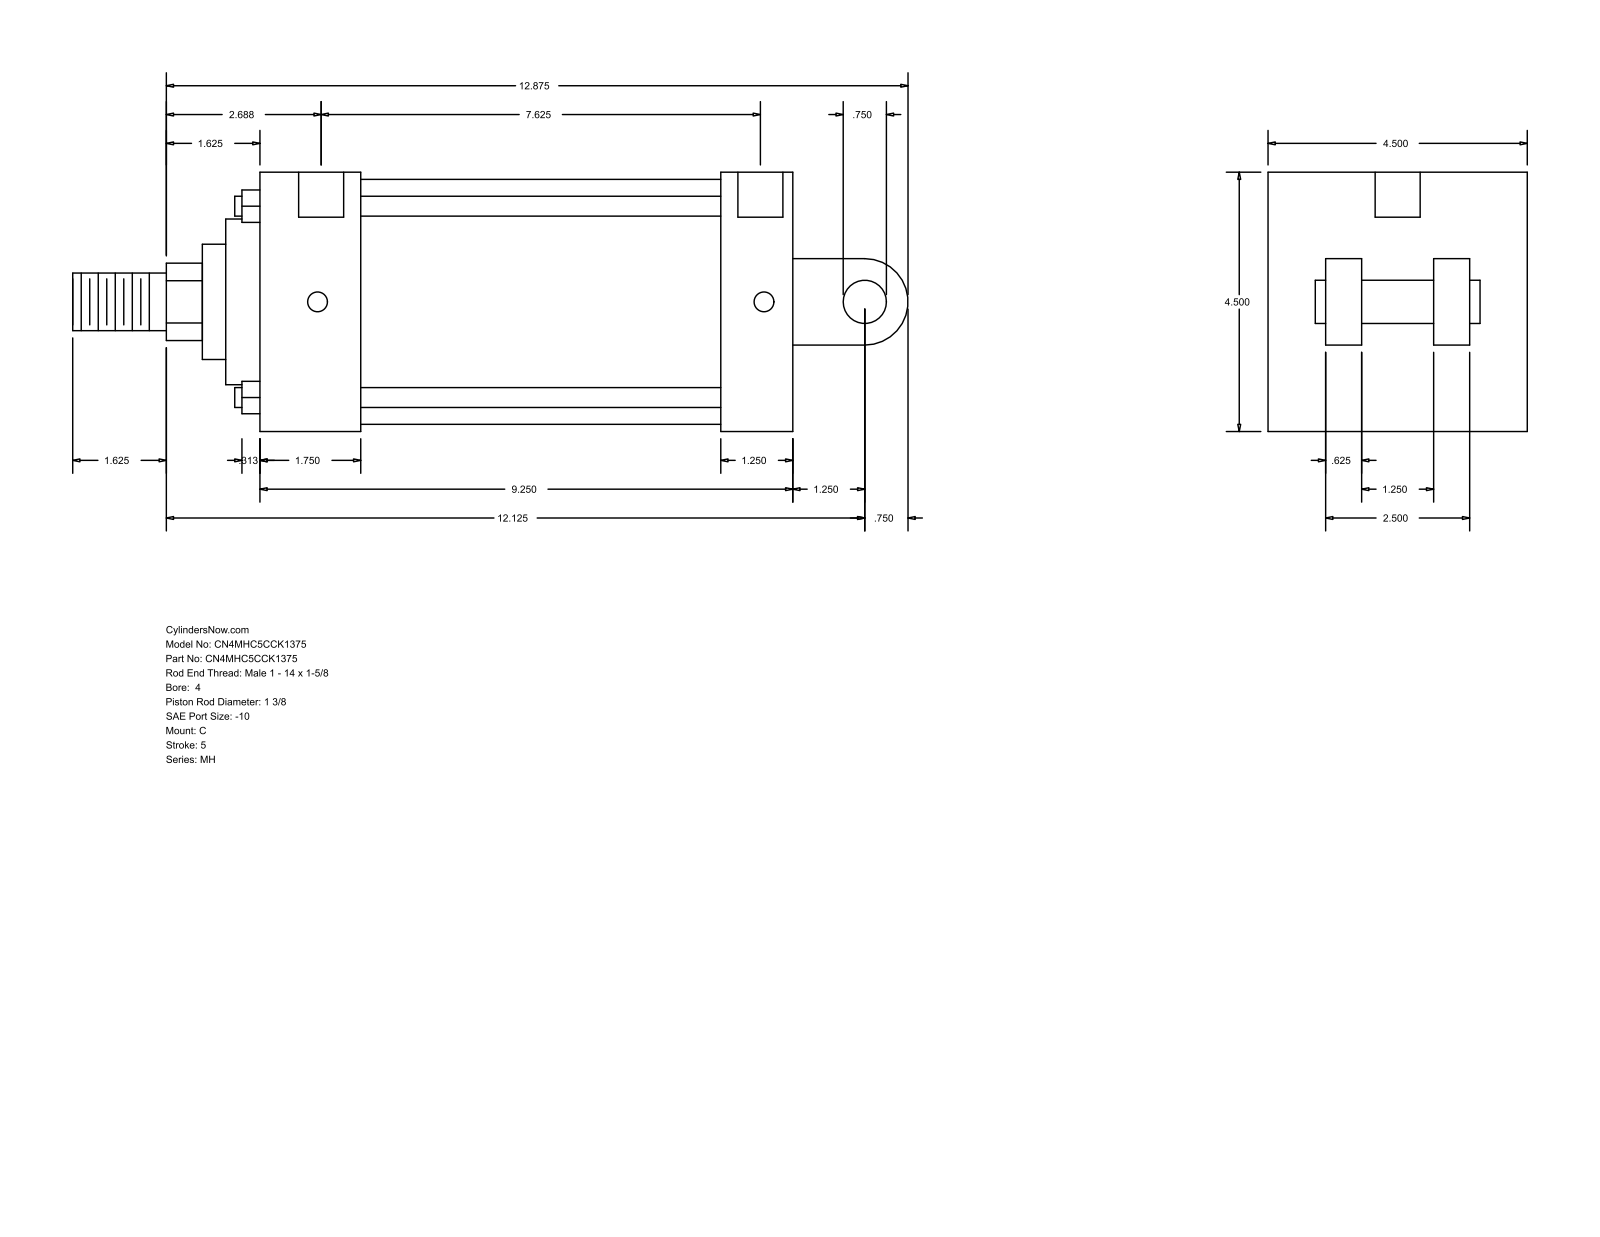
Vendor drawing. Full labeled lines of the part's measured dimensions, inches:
Part name (STEP PRODUCT): MH_C__0400_1.375
STEP written by: GSSL Pune (CONFIG_CONTROL_DESIGN)
Units: inches
Bodies: 0 solids, 101 faces (71 planar, 30 cylindrical, 0 other)
Overall size (bounding box): 14.5 × 4.5 × 4.5
Round holes (diameter × count): ⌀0.344 ×4, ⌀0.781 ×2
Round bosses / shafts (diameter × count): ⌀0.345 ×4, ⌀4.25 ×1, ⌀2.875 ×1, ⌀2 ×1, ⌀1.375 ×1, ⌀1 ×1, ⌀0.75 ×1
Partial cylindrical surfaces — rounded edges, fillets, slot ends (radius × count): R0.672 ×1, R0.75 ×1
Main face-to-face distances: 4.5, 9.25, 1.25, 1.75, 8, 6.25, 7.5, 1.625, 2.875, 1.5
Hole centre spacings: 7.75, 0.062, 0.063, 7.625, 7.687, 7.688
